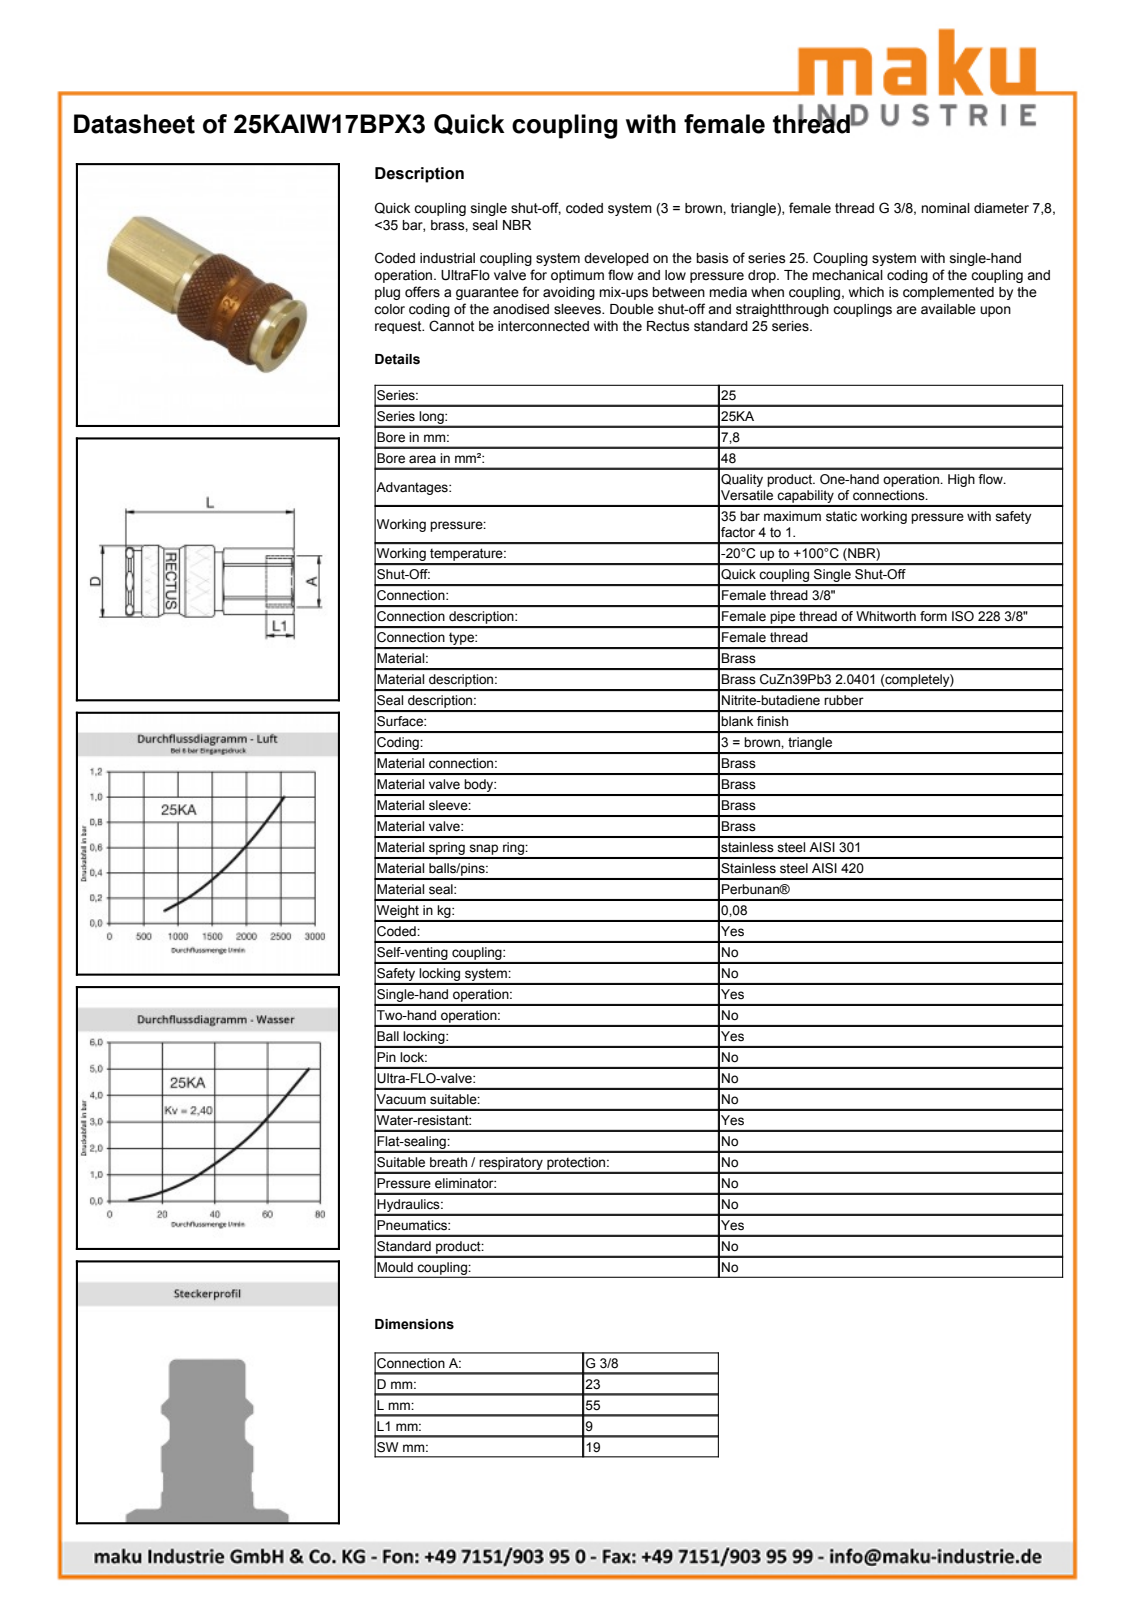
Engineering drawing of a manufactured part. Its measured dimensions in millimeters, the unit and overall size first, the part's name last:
Units: millimetres
Overall size (bounding box): 54.5 × 23.15 × 23.15
Round holes (diameter × count): ⌀14 ×1, ⌀14.95 ×1, ⌀16 ×1, ⌀17.25 ×1, ⌀19.35 ×1, ⌀20.05 ×1
Round bosses / shafts (diameter × count): ⌀23.15 ×1, ⌀21 ×1, ⌀20 ×1, ⌀18.95 ×1, ⌀15.3 ×1, ⌀15.12 ×1
Partial cylindrical surfaces — rounded edges, fillets, slot ends (radius × count): R7.9 ×1, R10.4 ×1, R10.7 ×1, R11 ×1
Main face-to-face distances: 19, 45.48, 24.5, 20.98, 54.5, 30, 9.02, 21, 28.7, 4.2
Volume: 16 115 mm³ · Surface area: 8 177 mm²
Bodies: 2 solids, 734 faces (251 planar, 84 cylindrical, 399 other)
Part name (STEP PRODUCT): D106611
STEP written by: Autodesk Inventor 2011 (AUTOMOTIVE_DESIGN)
